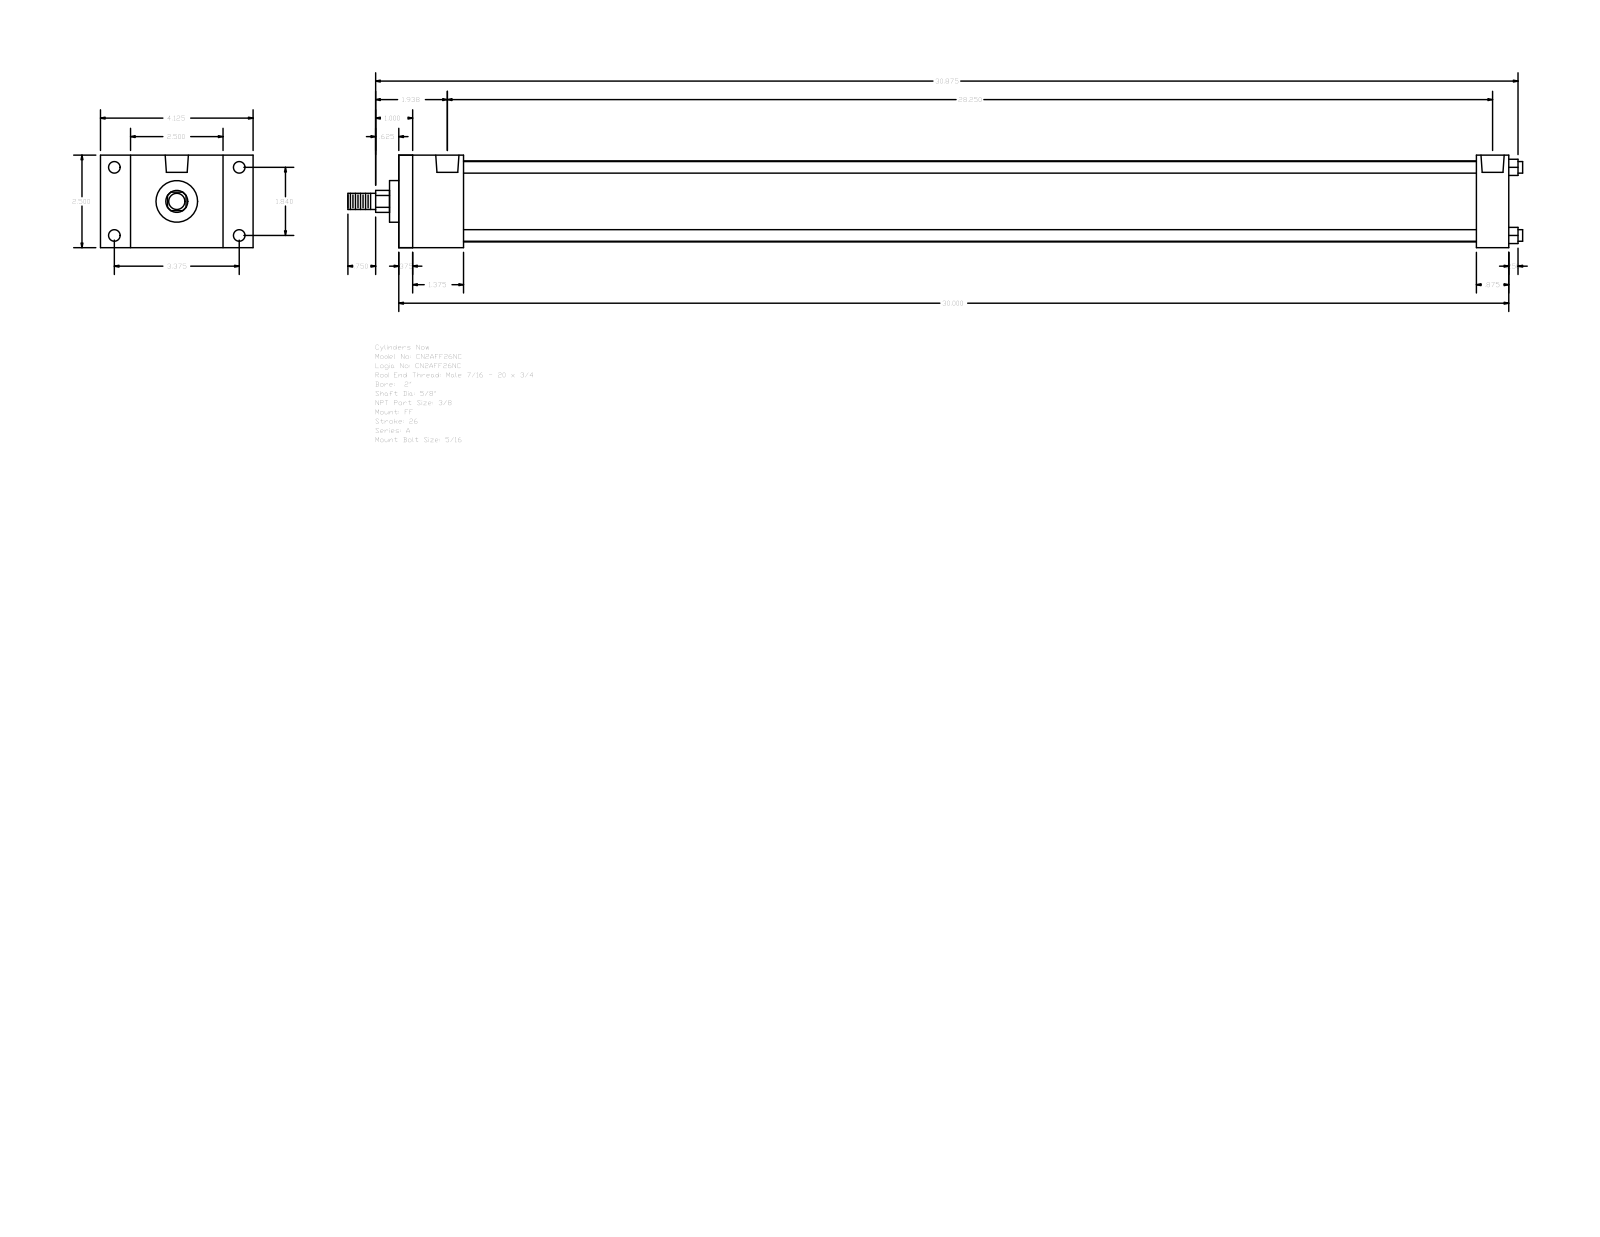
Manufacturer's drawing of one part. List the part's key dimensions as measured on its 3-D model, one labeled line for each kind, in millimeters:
Part name (STEP PRODUCT): A_FF__0200_0.625
STEP written by: GSSL Pune (CONFIG_CONTROL_DESIGN)
Units: millimetres
Bodies: 0 solids, 92 faces (64 planar, 28 cylindrical, 0 other)
Overall size (bounding box): 806.45 × 104.78 × 63.5
Round holes (diameter × count): ⌀5.56 ×4, ⌀7.94 ×4, ⌀15.93 ×2
Round bosses / shafts (diameter × count): ⌀7.94 ×4, ⌀55.63 ×1, ⌀28.57 ×1, ⌀15.88 ×1, ⌀11.11 ×1
Partial cylindrical surfaces — rounded edges, fillets, slot ends (radius × count): R7.54 ×1
Main face-to-face distances: 63.5, 762, 9.52, 752.48, 34.93, 44.45, 739.77, 730.25, 695.32, 717.55
Hole centre spacings: 46.74, 85.72, 97.63, 709.6, 3.97, 3.98, 713.57, 713.58
